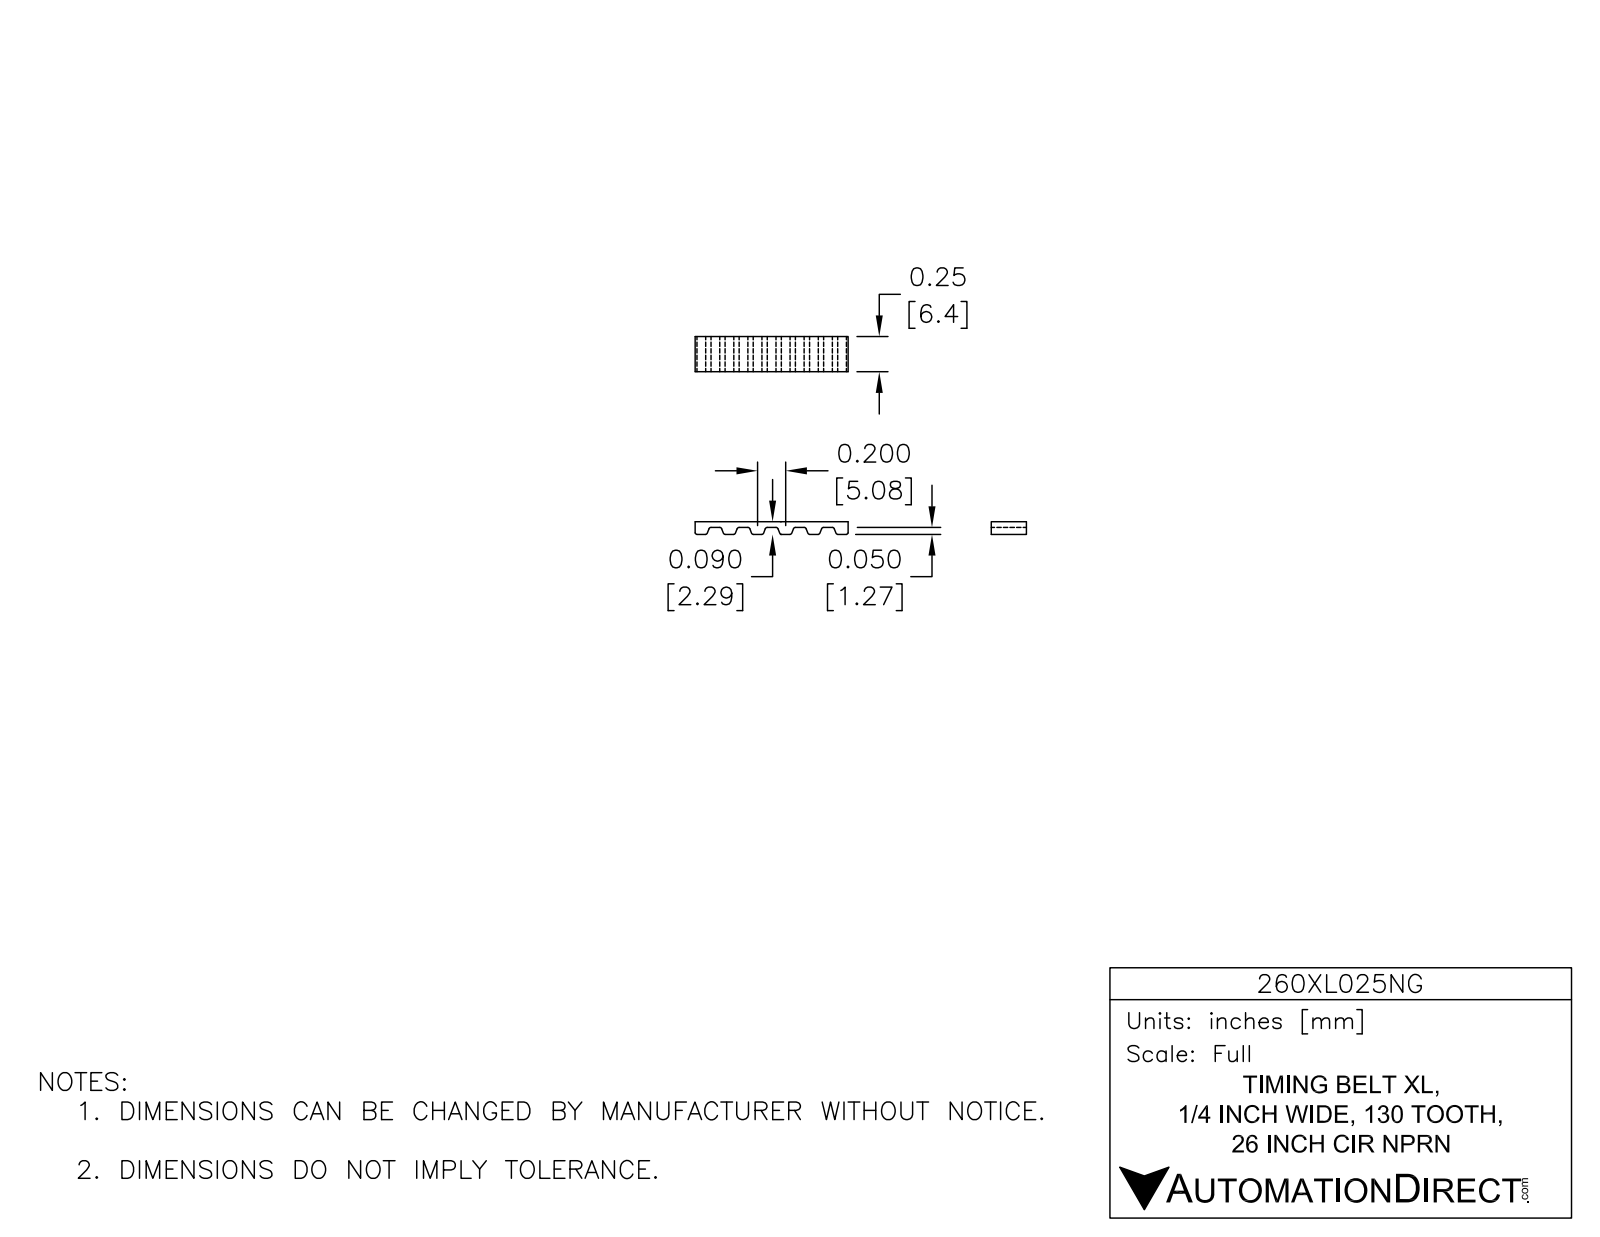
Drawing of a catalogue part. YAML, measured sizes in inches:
part_name: "260XL025NG"
step_written_by: "SolidWorks 2014 (AUTOMOTIVE_DESIGN)"
units: inches
bodies: {solids: 1, faces: 1076, planar: 478, cylindrical: 598, other: 0}
overall_size: [11.288, 3, 0.25]
volume: 0.354
surface_area: 17.56
partial_cylinders:
  - {radius: 0.015, count: 520}
  - {radius: 1.46, count: 2}
  - {radius: 1.5, count: 2}
face_to_face_distances: [3, 0.04, 2.96, 0.25, 2.92, 0.09, 2.91, 0.05, 2.87, 2.82]
